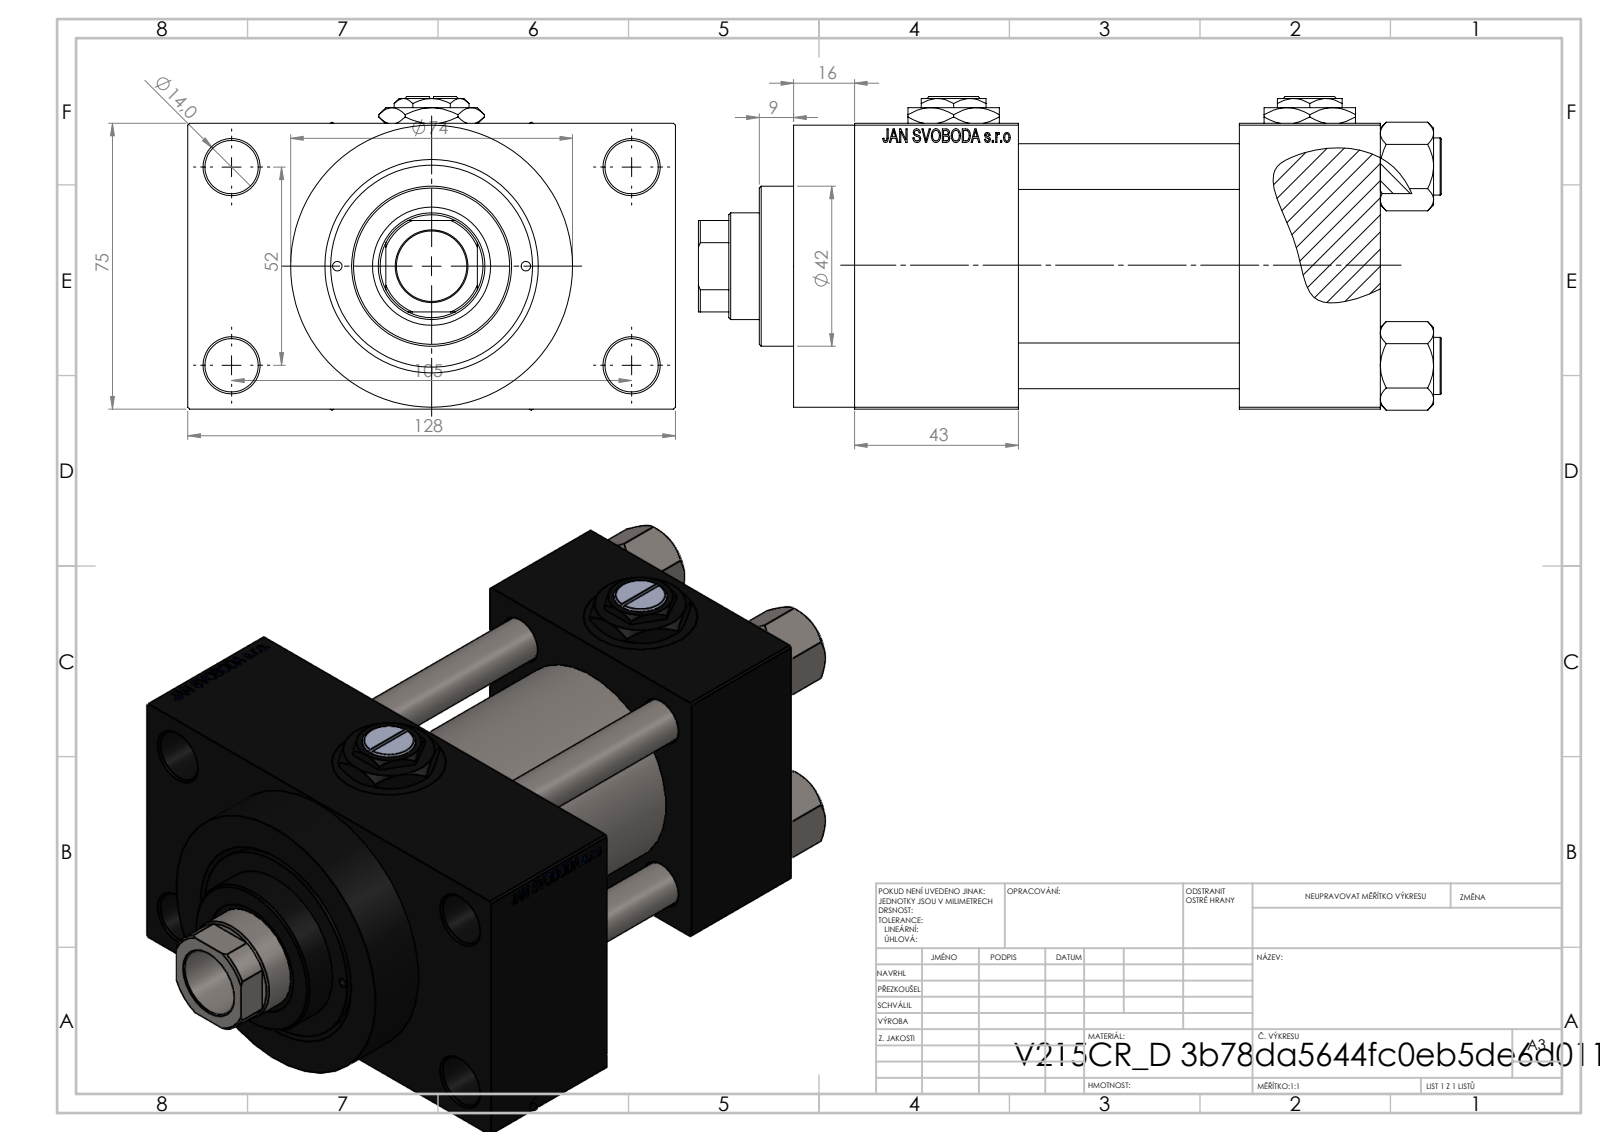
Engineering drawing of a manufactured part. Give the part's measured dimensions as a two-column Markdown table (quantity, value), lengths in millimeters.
| quantity | value |
| --- | --- |
| part name | NUT_M5_D; V215CR_D_Body; V215CR_D_TYCINKA; Zatka_pro_OIL_PORT (+2 more) |
| STEP written by | SolidWorks 2019 (CONFIG_CONTROL_DESIGN) |
| units | millimeters |
| bodies | 13 solids, 1212 faces (547 planar, 103 cylindrical, 562 other) |
| overall size | 195 × 128 × 82.27 |
| volume | 801 583 mm³ |
| surface area | 174 777 mm² |
| round holes (diameter × count) | 12 × 4, 14 × 4, 20.96 × 4, 30 × 4, 7 × 3, 2.5 × 2, 18.5 × 1, 28 × 1, 31 × 1, 41 × 1, 50 × 1, 53 × 1 |
| round bosses / shafts (diameter × count) | 15 × 4, 74 × 1, 56 × 1, 42 × 1 |
| partial cylindrical surfaces (radius × count) | 13.5 × 1 |
| main face-to-face distances | 75, 58, 37, 95, 26.5, 138, 101, 43, 101.5, 16 |
| hole center spacings | 26.19, 26.35, 36.98, 38.03, 52.3, 57.22, 58.43, 58.59 |
